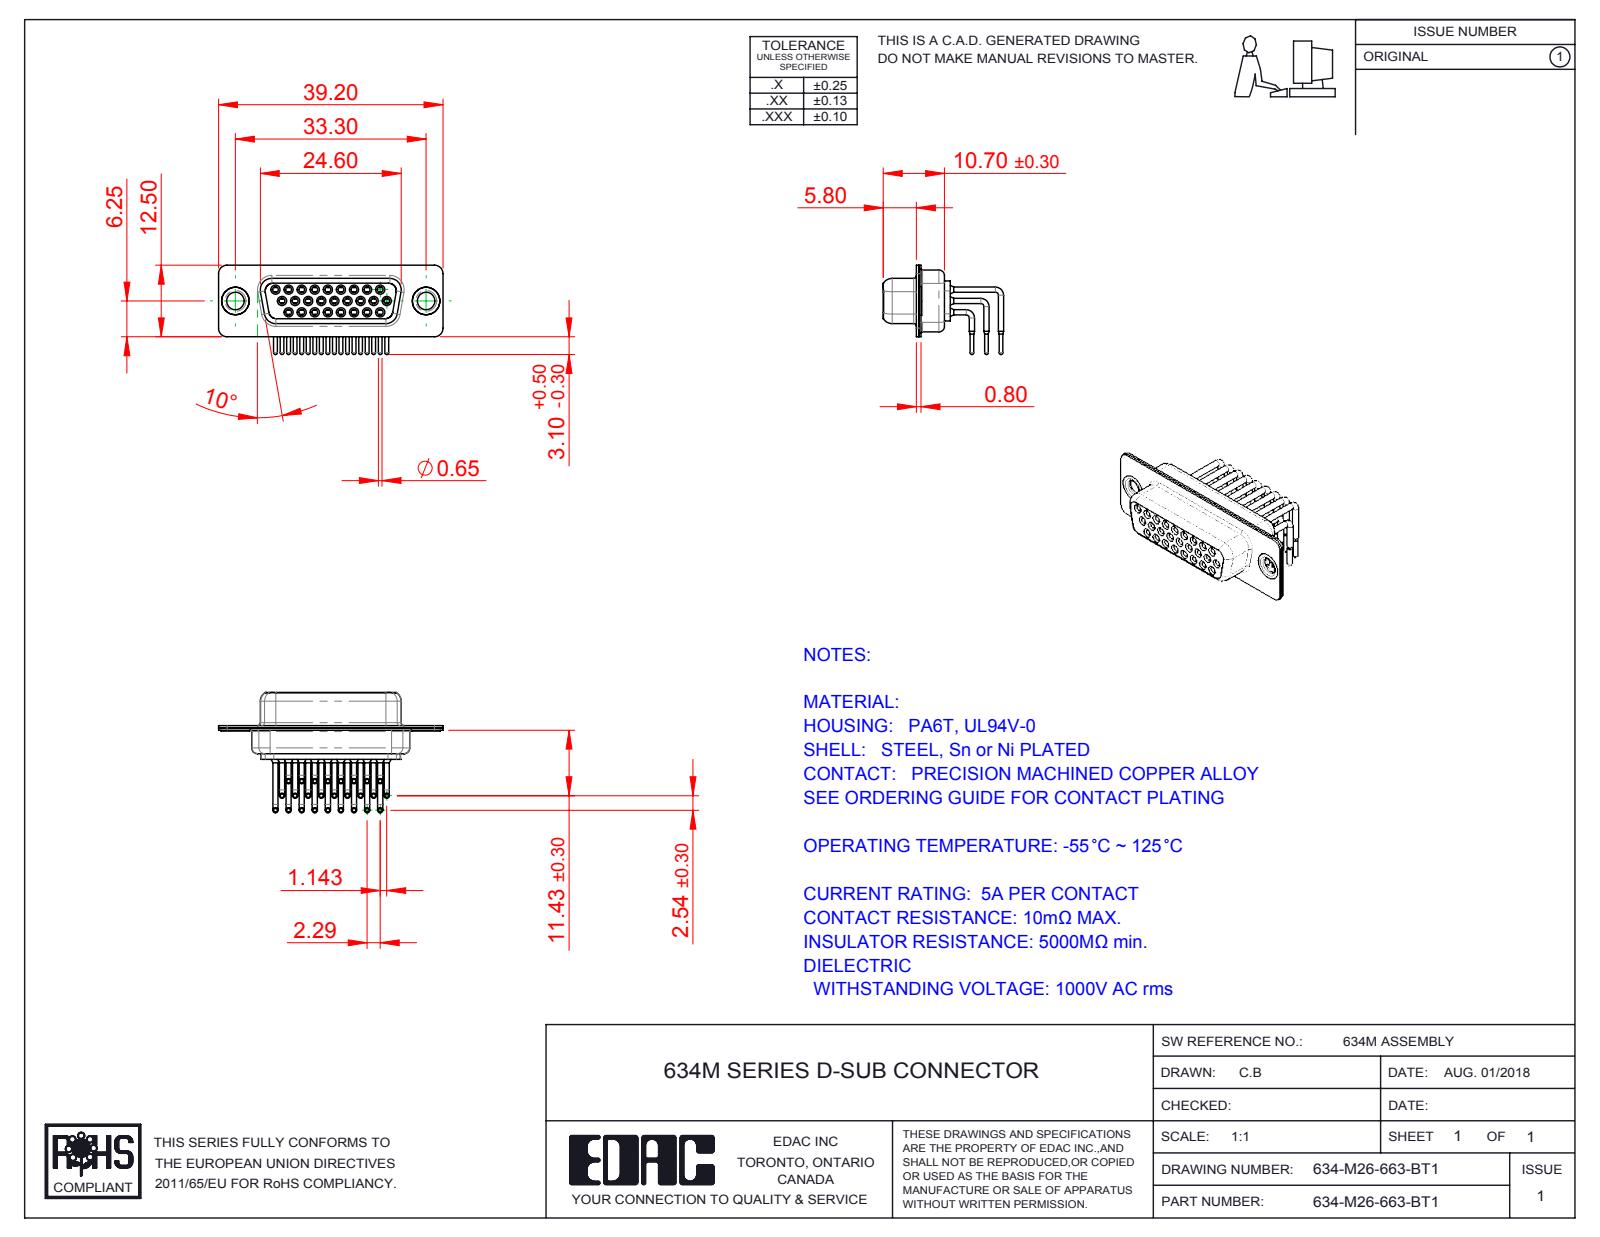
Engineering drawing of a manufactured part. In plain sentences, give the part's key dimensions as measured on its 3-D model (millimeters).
The part is named "634M Thru Hole Rivet; 634-M26-663-BT1; 634M Shell Rear_26 Contacts; 634M Shell Front_26 Contacts (+4 more)". Its 3-D file was written by "SolidWorks 2016 (CONFIG_CONTROL_DESIGN)". It is 31 solids with 1631 faces: 457 planar, 719 cylindrical and 455 other. Overall it measures 39.2 by 21.02 by 15.6 millimeters. Its volume is 2 454 cubic millimeters and its surface area 8 321 square millimeters. Round holes: 26 of diameter 1, 26 of diameter 1.1, 26 of diameter 1.7, 26 of diameter 1.8, 26 of diameter 2, 2 of diameter 3.05, 2 of diameter 4, 2 of diameter 4.8. Round bosses or shafts: 52 of diameter 0.9, 26 of diameter 1.6, 26 of diameter 1.5, 26 of diameter 0.65, 2 of diameter 5, 2 of diameter 4.9, 2 of diameter 3.55, 1 of diameter 2. Partial cylindrical surfaces (rounded edges, fillets, slot ends): 16 of radius 1.5, 12 of radius 2, 8 of radius 1.35, 8 of radius 1.6, 4 of radius 0.25, 4 of radius 0.5, 4 of radius 0.6, 4 of radius 0.65. The main face-to-face distances are 0.4, 1.45, 8.95, 8.5, 1.9, 2.3, 0.8, 6.2, 0.45, 7.05. The hole center spacings are 3.96, 2.28, 4.57, 6.05, 2.29, 8.24, 6.86, 6.04.
